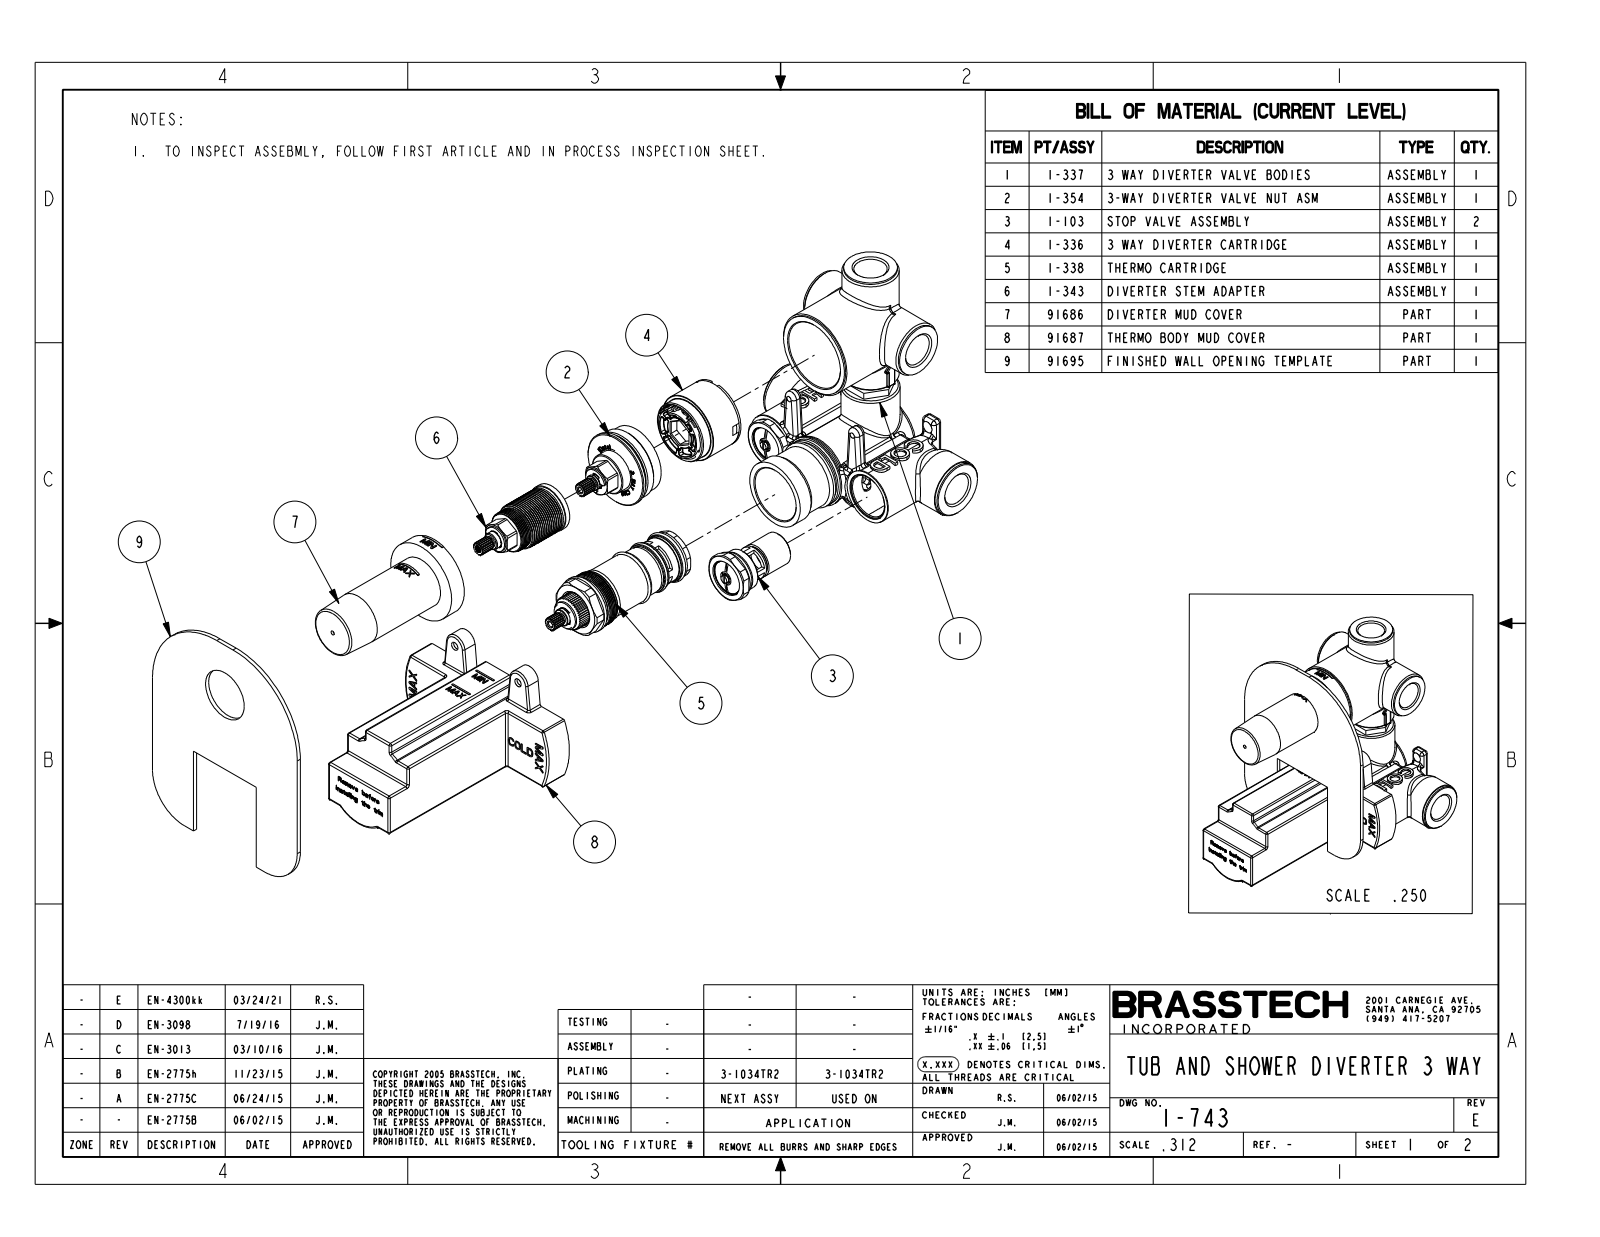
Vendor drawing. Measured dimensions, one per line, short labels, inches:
name: 1-743_SW0002
written by: CREO PARAMETRIC BY PTC INC, 2018400 (CONFIG_CONTROL_DESIGN)
unit: in
bodies: 1 solid, 1875 faces (941 planar, 390 cylindrical, 544 other)
size: 6.343 × 5.433 × 4.791
volume: 28.64 in³; area: 102.9 in²
holes: 4× ⌀0.13, 2× ⌀0.276, 2× ⌀0.315, 2× ⌀0.693, 2× ⌀0.807, 2× ⌀0.827, 1× ⌀0.394
bosses: 3× ⌀1.26, 2× ⌀1.299, 2× ⌀1.181, 2× ⌀0.945, 2× ⌀0.785, 2× ⌀0.598, 2× ⌀0.256, 2× ⌀0.236
rounds: 43× R0.079, 34× R0.02, 4× R0.039, 2× R0.069, 2× R0.154, 2× R0.157, 2× R0.207, 2× R0.295
face distances: 4.213, 1.22, 0.079, 1.87, 1.063, 2.992, 2.488, 5.433, 0.067, 2.146
hole spacings: 0.677, 0.835, 1.47, 1.496, 1.607, 1.693, 2.027, 2.426
